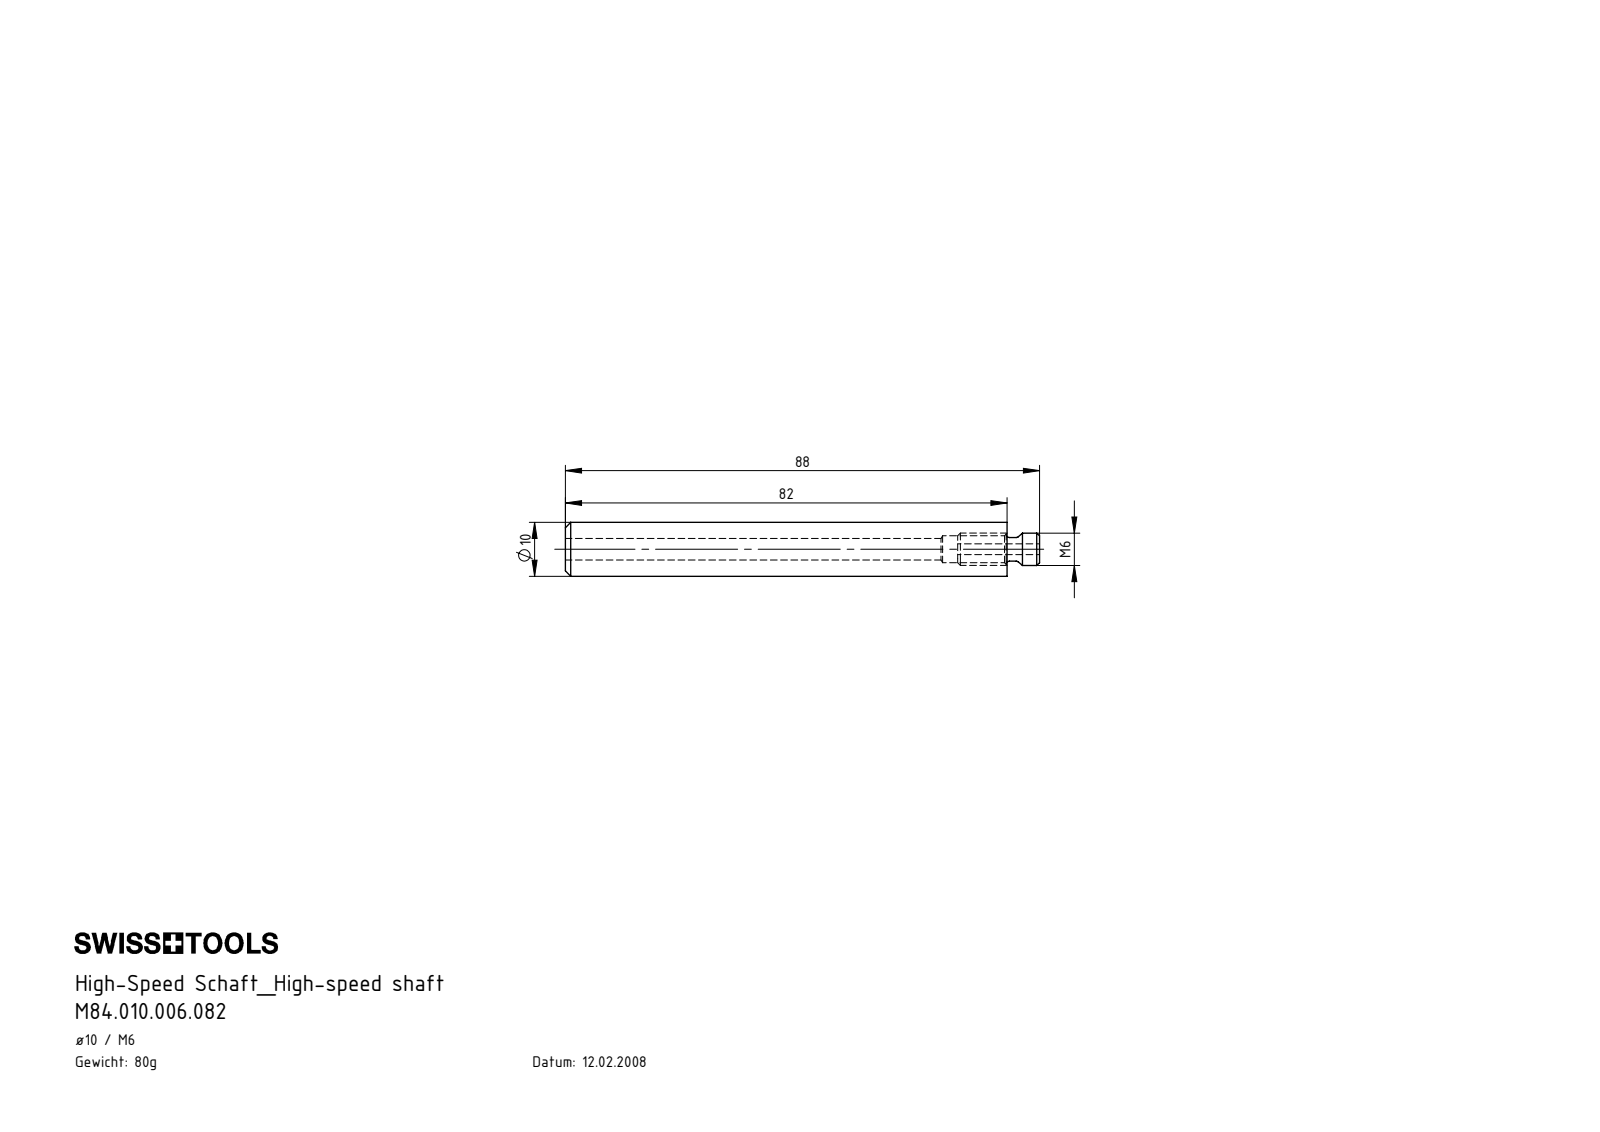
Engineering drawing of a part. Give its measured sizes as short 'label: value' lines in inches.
name: HM1-U10.001.082_A; U10.HS6.K01.082; HM1-BG1.006.015_A
written by: SolidWorks 2017 (AUTOMOTIVE_DESIGN)
unit: in
bodies: 2 solids, 20 faces (5 planar, 7 cylindrical, 8 other)
size: 3.465 × 0.394 × 0.394
volume: 0.345 in³; area: 6.465 in²
holes: 1× ⌀0.079, 1× ⌀0.157, 1× ⌀0.197
bosses: 1× ⌀0.394, 1× ⌀0.236, 1× ⌀0.173
face distances: 3.228, 2.866, 0.362, 3.465, 0.598, 0.236, 3.22, 0.354, 0.244
